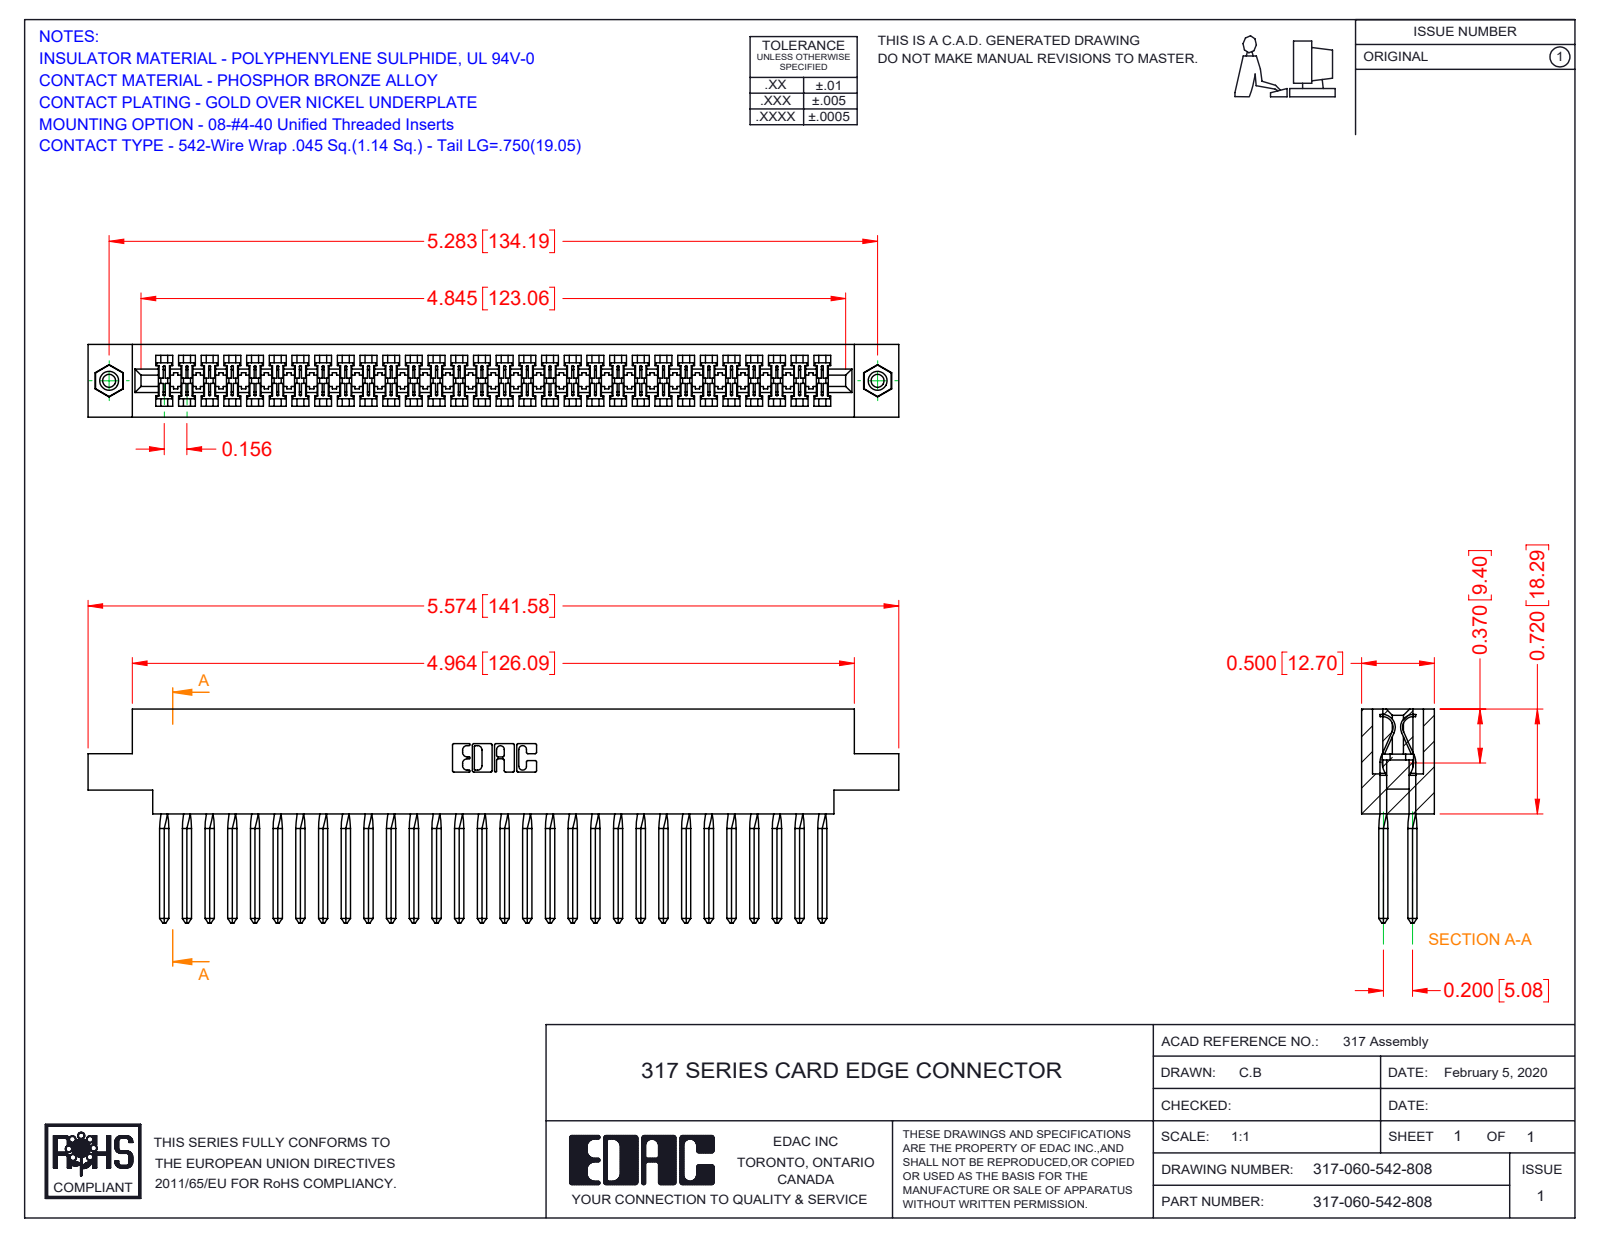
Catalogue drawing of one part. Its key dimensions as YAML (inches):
part_name: "317-060-542-878; 345-250-001_345-250-003-102; 317-290-003_542; 317 Part_.156 Dia - TI"
step_written_by: "SolidWorks 2016 (CONFIG_CONTROL_DESIGN)"
units: inches
bodies: {solids: 63, faces: 3582, planar: 2850, cylindrical: 476, other: 256}
overall_size: [5.574, 1.47, 0.5]
volume: 1.391
surface_area: 48.58
round_holes:
  - {diameter: 0.089, count: 2}
  - {diameter: 0.125, count: 2}
  - {diameter: 0.156, count: 2}
round_bosses_or_shafts:
  - {diameter: 0.155, count: 2}
partial_cylinders:
  - {radius: 0.006, count: 120}
  - {radius: 0.01, count: 22}
  - {radius: 0.007, count: 6}
  - {radius: 0.031, count: 6}
  - {radius: 0.026, count: 3}
  - {radius: 0.074, count: 2}
  - {radius: 0.089, count: 2}
  - {radius: 0.1, count: 2}
face_to_face_distances: [0.5, 0.075, 0.425, 0.35, 0.2, 0.11, 0.116, 0.046, 0.136, 0.128]
hole_center_spacings: [5.283]
